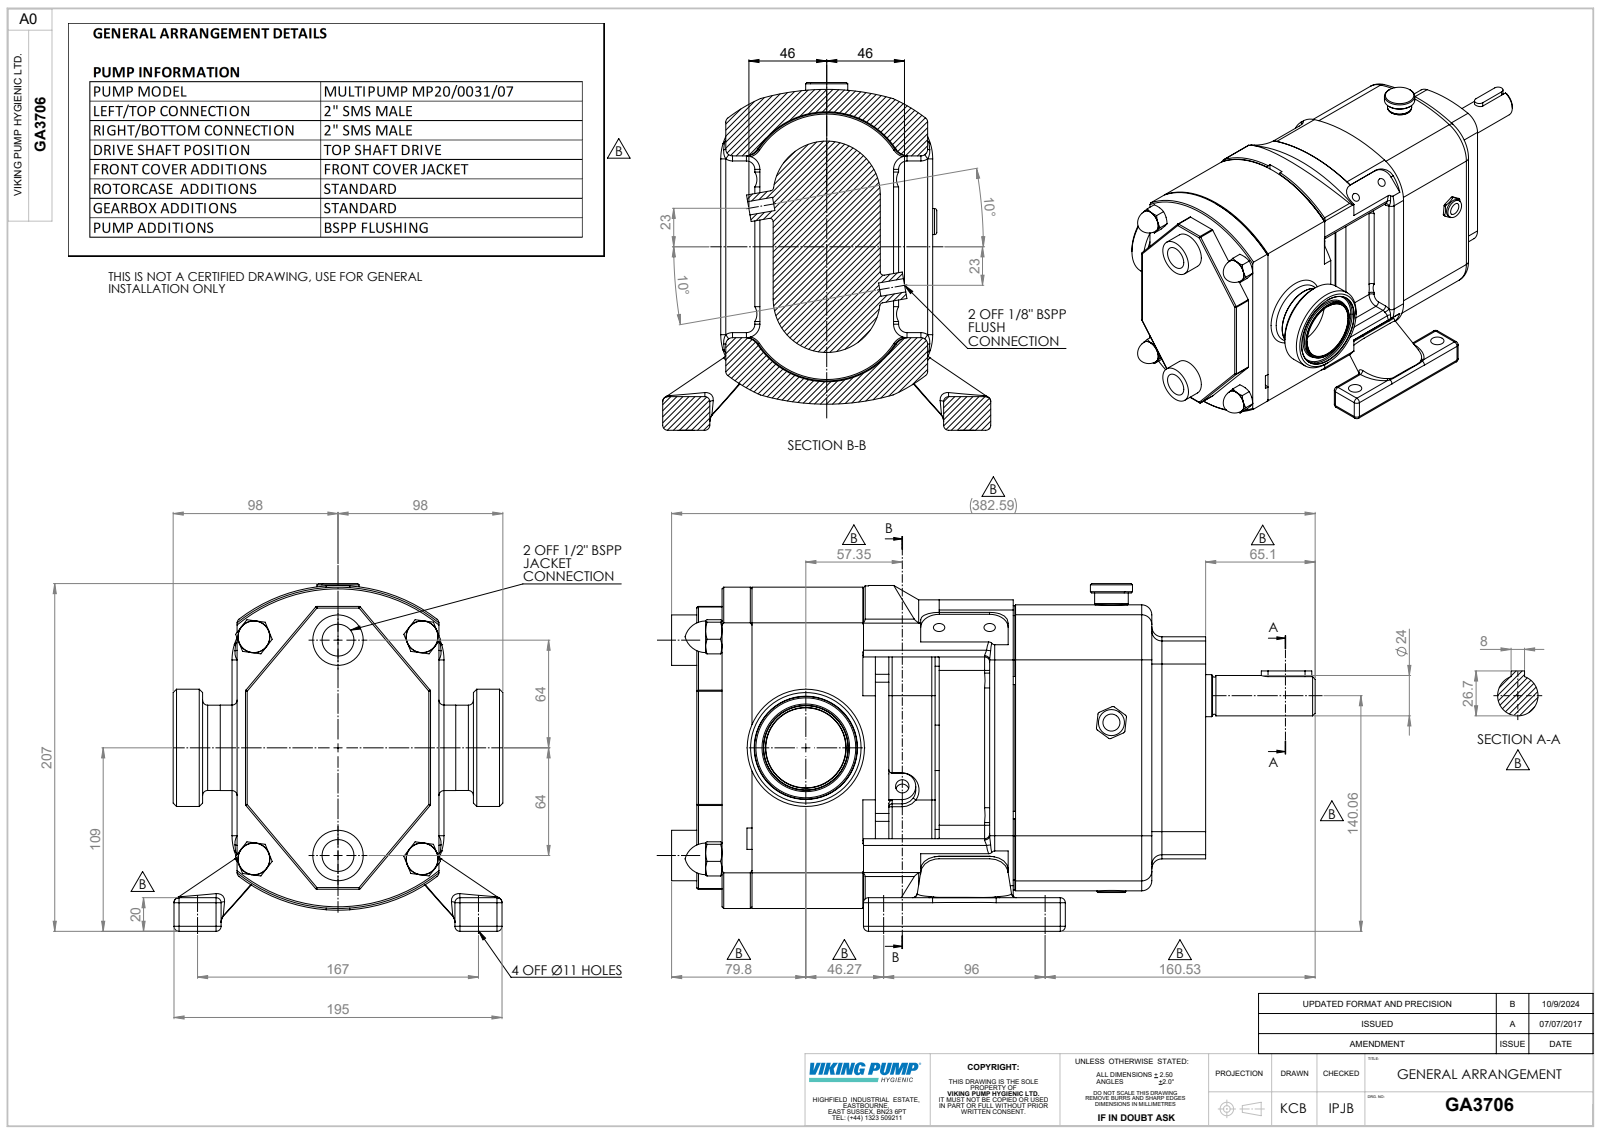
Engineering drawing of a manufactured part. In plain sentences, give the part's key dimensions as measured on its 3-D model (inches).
The part is named "Copy of CP20-0031-07 H T^GA3706; GA3706; Copy of Z94-5101-33 - 2 INCH SMS681^GA3706; Copy of CP-MP20 Half Inch BSP Jacket^GA3706". Its 3-D file was written by "SolidWorks 2023 (AUTOMOTIVE_DESIGN)". It is 4 solids with 901 faces: 271 planar, 321 cylindrical and 309 other. Overall it measures 15.063 by 8.137 by 7.717 inches. Its volume is 334.5 cubic inches and its surface area 559.5 square inches. Round holes: 4 of diameter 0.268, 4 of diameter 0.433, 3 of diameter 0.255, 2 of diameter 0.315, 2 of diameter 0.747, 1 of diameter 0.887, 1 of diameter 1.874, 1 of diameter 2.402. Round bosses or shafts: 2 of diameter 1.378, 2 of diameter 1.181, 2 of diameter 0.669, 1 of diameter 2.744, 1 of diameter 2, 1 of diameter 1.996, 1 of diameter 1.988, 1 of diameter 0.985. Partial cylindrical surfaces (rounded edges, fillets, slot ends): 52 of radius 0.118, 28 of radius 0.039, 18 of radius 0.079, 8 of radius 0.236, 8 of radius 0.437, 6 of radius 0.05, 6 of radius 0.157, 6 of radius 0.315. The main face-to-face distances are 4.724, 0.591, 5.082, 5.673, 6.236, 11.319, 11.909, 0.394, 0.984, 3.74. The hole center spacings are 1.183, 2.114, 2.52, 3.78, 6.575, 7.584, 1.261, 1.262.
